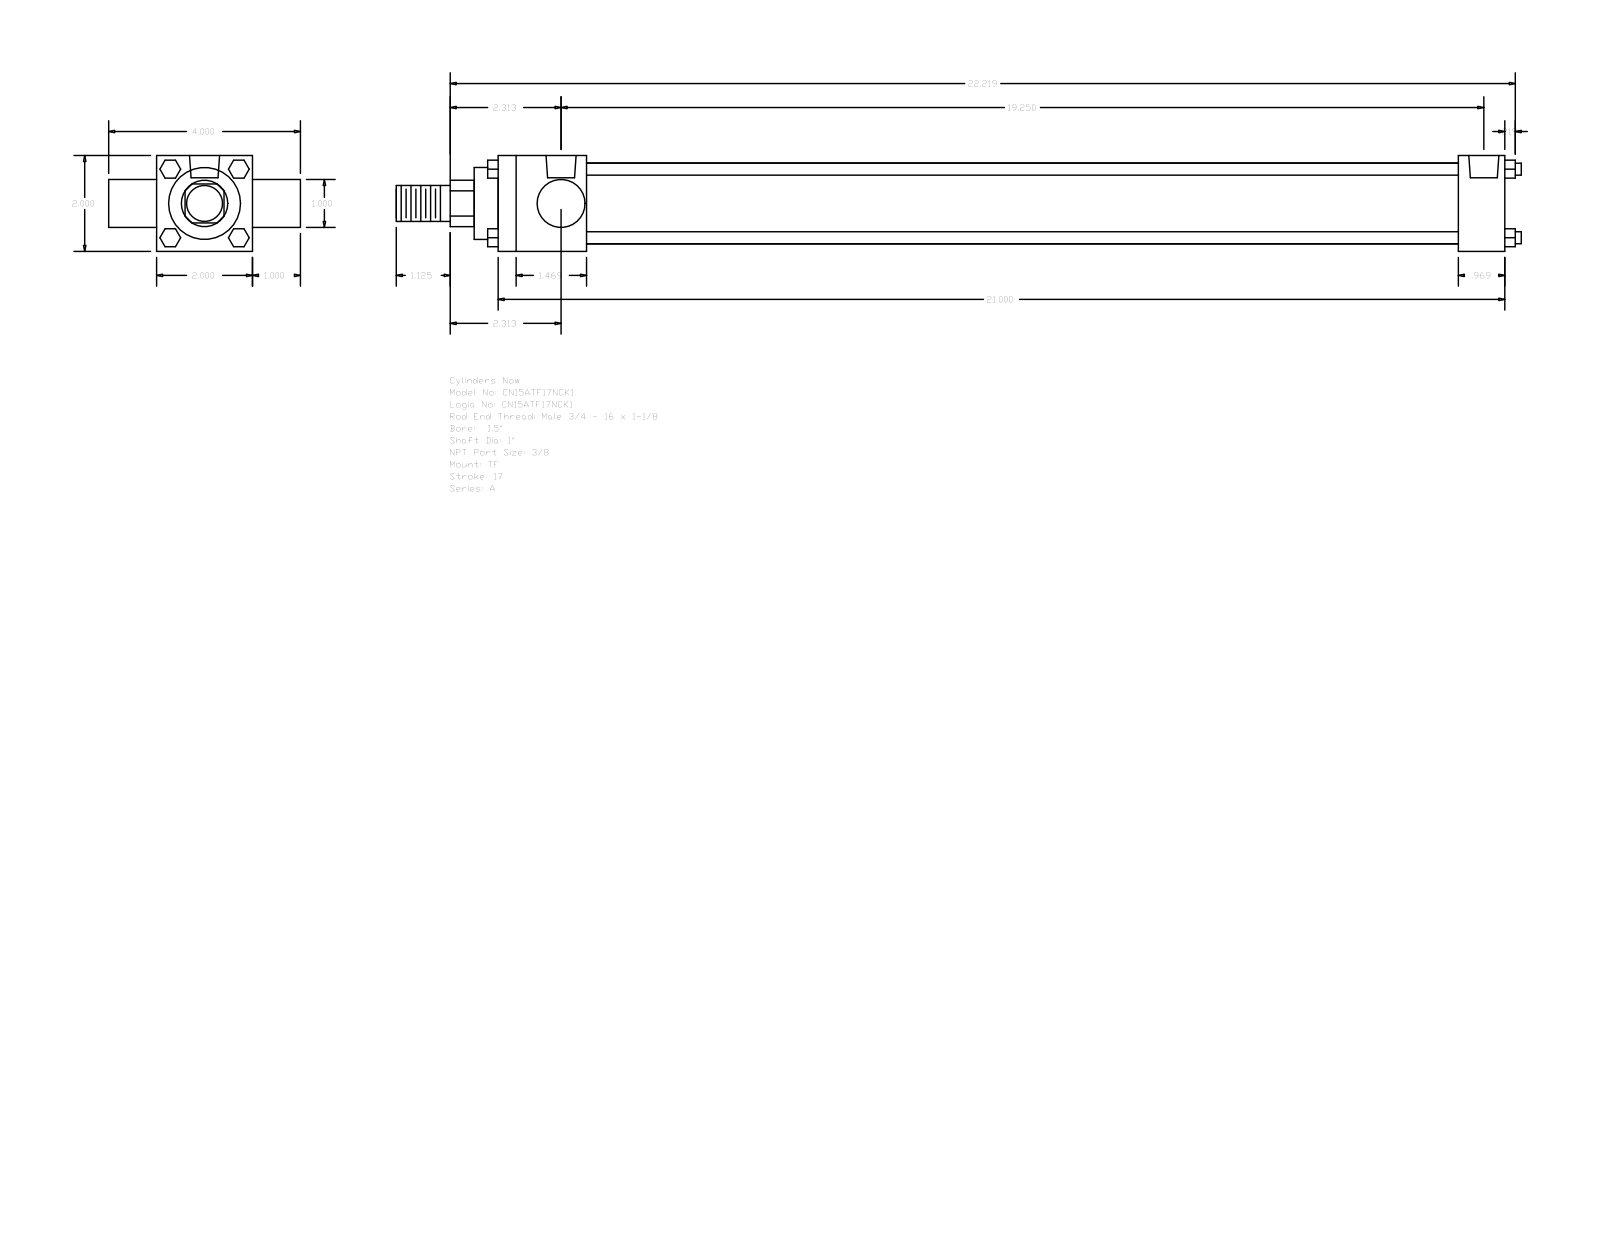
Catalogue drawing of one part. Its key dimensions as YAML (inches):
part_name: "A_TF__0150_1"
step_written_by: "GSSL Pune (CONFIG_CONTROL_DESIGN)"
units: inches
bodies: {solids: 0, faces: 120, planar: 92, cylindrical: 28, other: 0}
overall_size: [23.469, 4, 2]
round_holes:
  - {diameter: 0.219, count: 3}
  - {diameter: 0.627, count: 2}
round_bosses_or_shafts:
  - {diameter: 0.25, count: 4}
  - {diameter: 1, count: 2}
  - {diameter: 1.69, count: 1}
  - {diameter: 1.5, count: 1}
  - {diameter: 0.75, count: 1}
partial_cylinders:
  - {radius: 0.484, count: 1}
face_to_face_distances: [2, 1, 21, 3, 1.844, 20.031, 18.187, 19.156, 0.969, 0.5]
hole_center_spacings: [0.156, 19.094, 18.937, 19.25]
